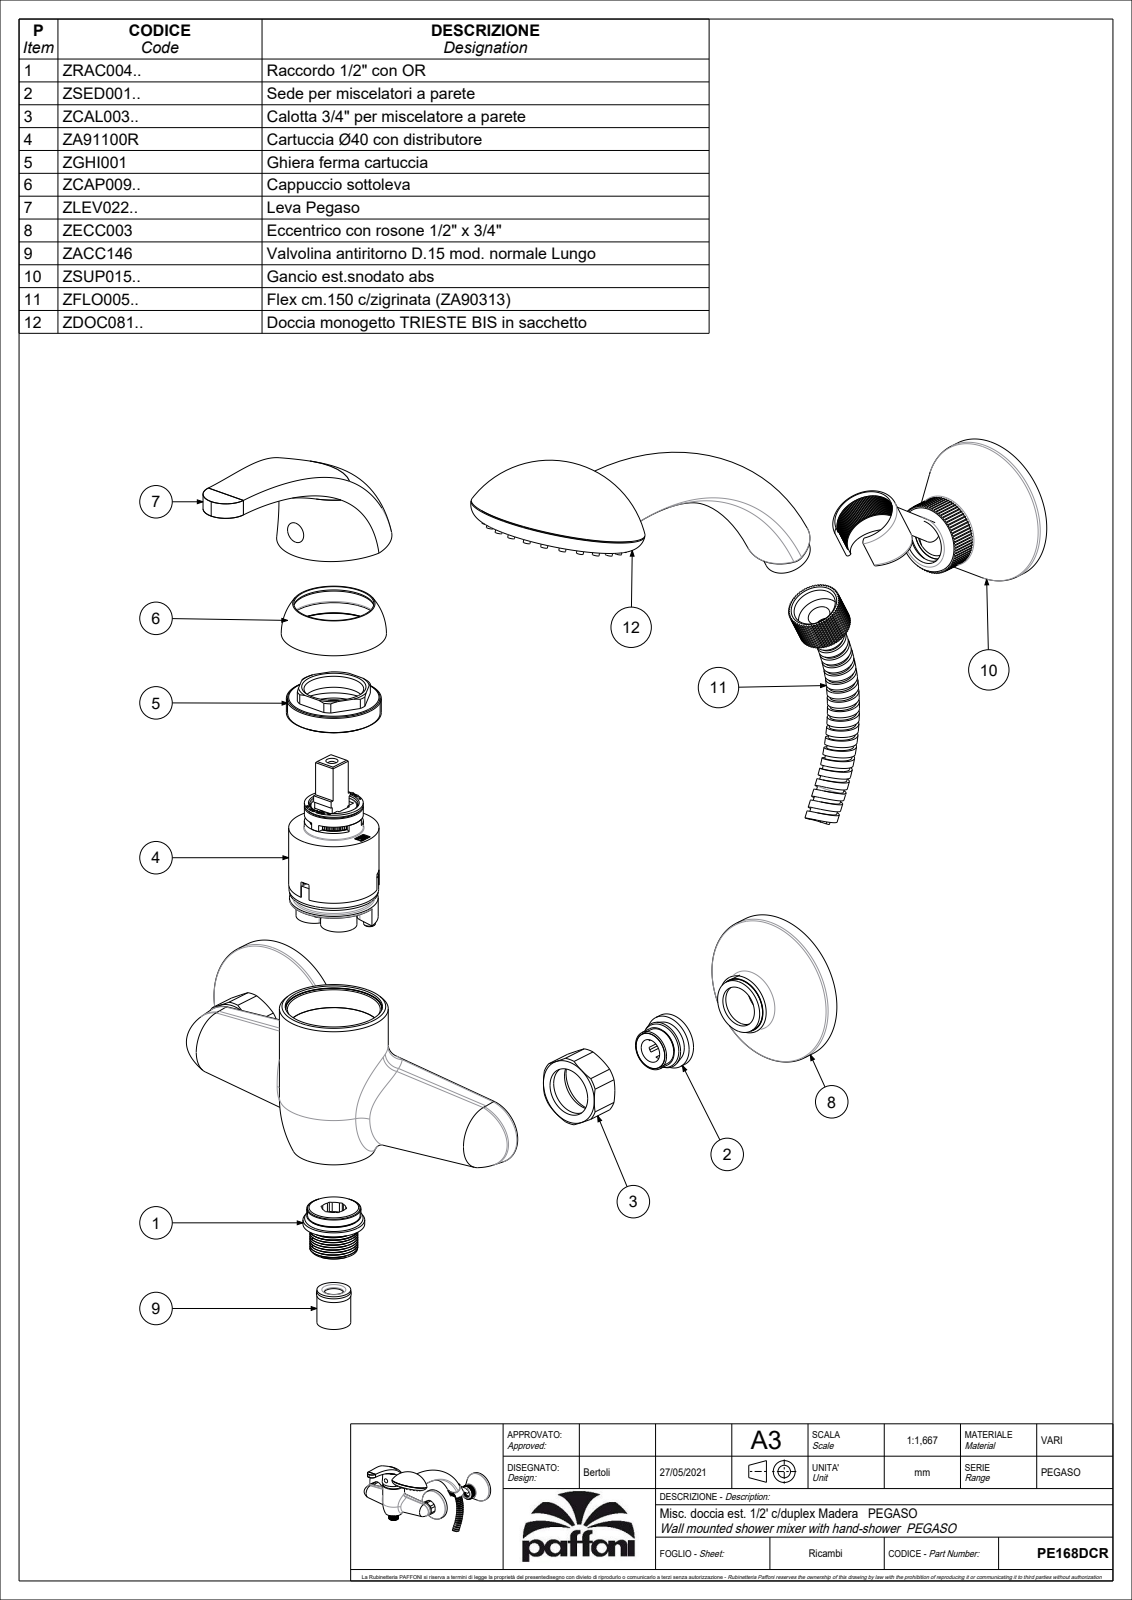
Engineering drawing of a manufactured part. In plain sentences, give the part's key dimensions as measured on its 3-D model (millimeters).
The part is named "PE168DCR_SW0001". Its 3-D file was written by "CREO PARAMETRIC BY PTC INC, 2022124 (CONFIG_CONTROL_DESIGN)". It is 6 solids with 1619 faces: 491 planar, 603 cylindrical and 525 other. Overall it measures 318.24 by 280.07 by 277.8 millimeters. Its volume is 485 129 cubic millimeters and its surface area 174 515 square millimeters. Round holes: 3 of diameter 10, 3 of diameter 19, 2 of diameter 5.5, 2 of diameter 6, 2 of diameter 7, 2 of diameter 15, 2 of diameter 16.7, 2 of diameter 20.3, 2 of diameter 21.5, 2 of diameter 24.1, 2 of diameter 26.7, 1 of diameter 4. Round bosses or shafts: 3 of diameter 21, 2 of diameter 66, 2 of diameter 26.4, 2 of diameter 10, 1 of diameter 75.5, 1 of diameter 64, 1 of diameter 47.6, 1 of diameter 29.5. Partial cylindrical surfaces (rounded edges, fillets, slot ends): 95 of radius 0.25, 72 of radius 0.5, 8 of radius 1, 2 of radius 3.65, 2 of radius 3.8, 2 of radius 15.5, 2 of radius 15.89, 2 of radius 16.04. The main face-to-face distances are 34.5, 7.5, 11.5, 20.5, 1.5, 34.45, 4, 9.5, 9, 29. The hole center spacings are 8.6, 15.62, 15.81, 24.21, 97.31, 150, 14, 24.
